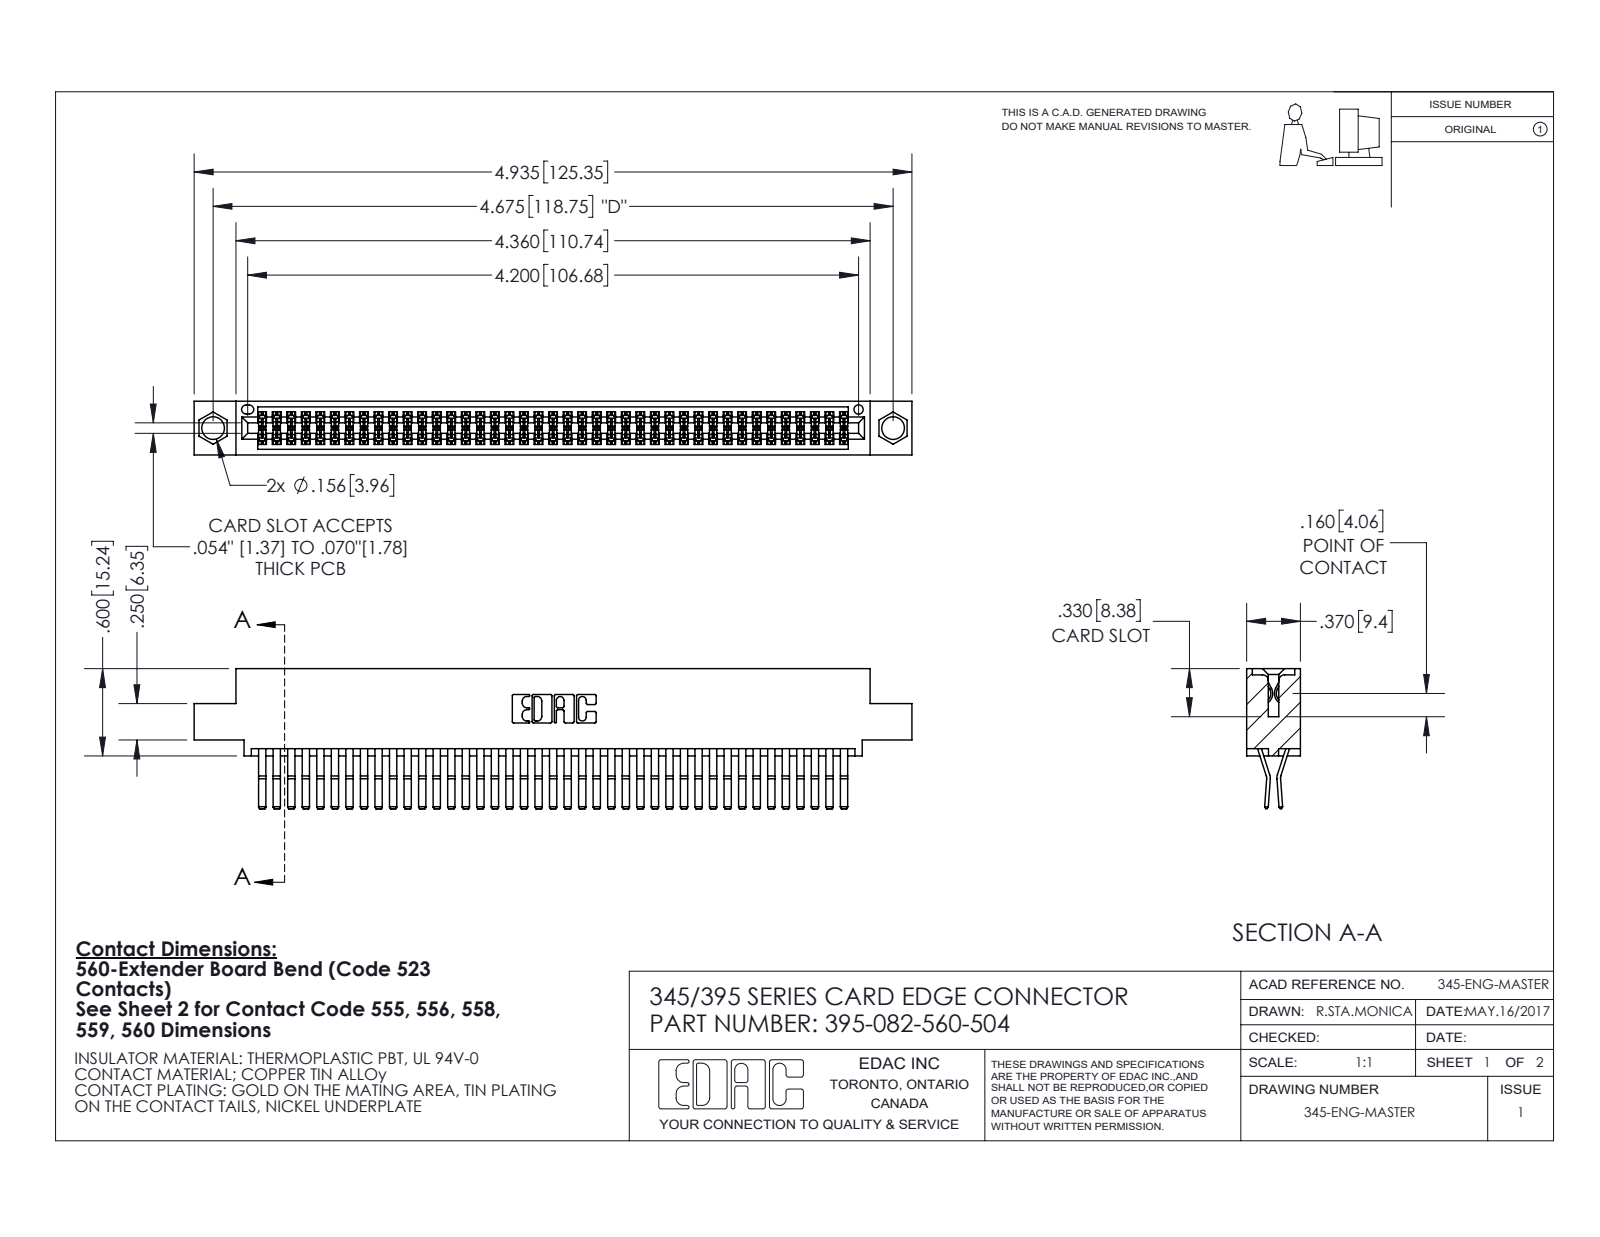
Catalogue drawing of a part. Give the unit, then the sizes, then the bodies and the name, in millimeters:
Units: millimetres
Overall size (bounding box): 125.3 × 24.4 × 9.4
Round holes (diameter × count): ⌀4 ×2, ⌀1.6 ×1
Partial cylindrical surfaces — rounded edges, fillets, slot ends (radius × count): R0.2 ×123, R0.3 ×22, R0.2 ×6, R0.8 ×6, R0.7 ×3, R0.3 ×2, R0.4 ×2, R0.5 ×2
Main face-to-face distances: 0.6, 7.6, 1.8, 9.4, 5.1, 2.5, 6.9, 5.7, 4.4, 3.8
Hole centre spacings: 6.9, 112.8, 118.7
Volume: 12 500 mm³ · Surface area: 19 820 mm²
Bodies: 83 solids, 4408 faces (2804 planar, 1604 cylindrical, 0 other)
Part name (STEP PRODUCT): 345-292-001_560 Tail; 345 Part_0.110 Offset - 0.156 Dia-TI; 395-082-560-504
STEP written by: SolidWorks 2020 (CONFIG_CONTROL_DESIGN)
